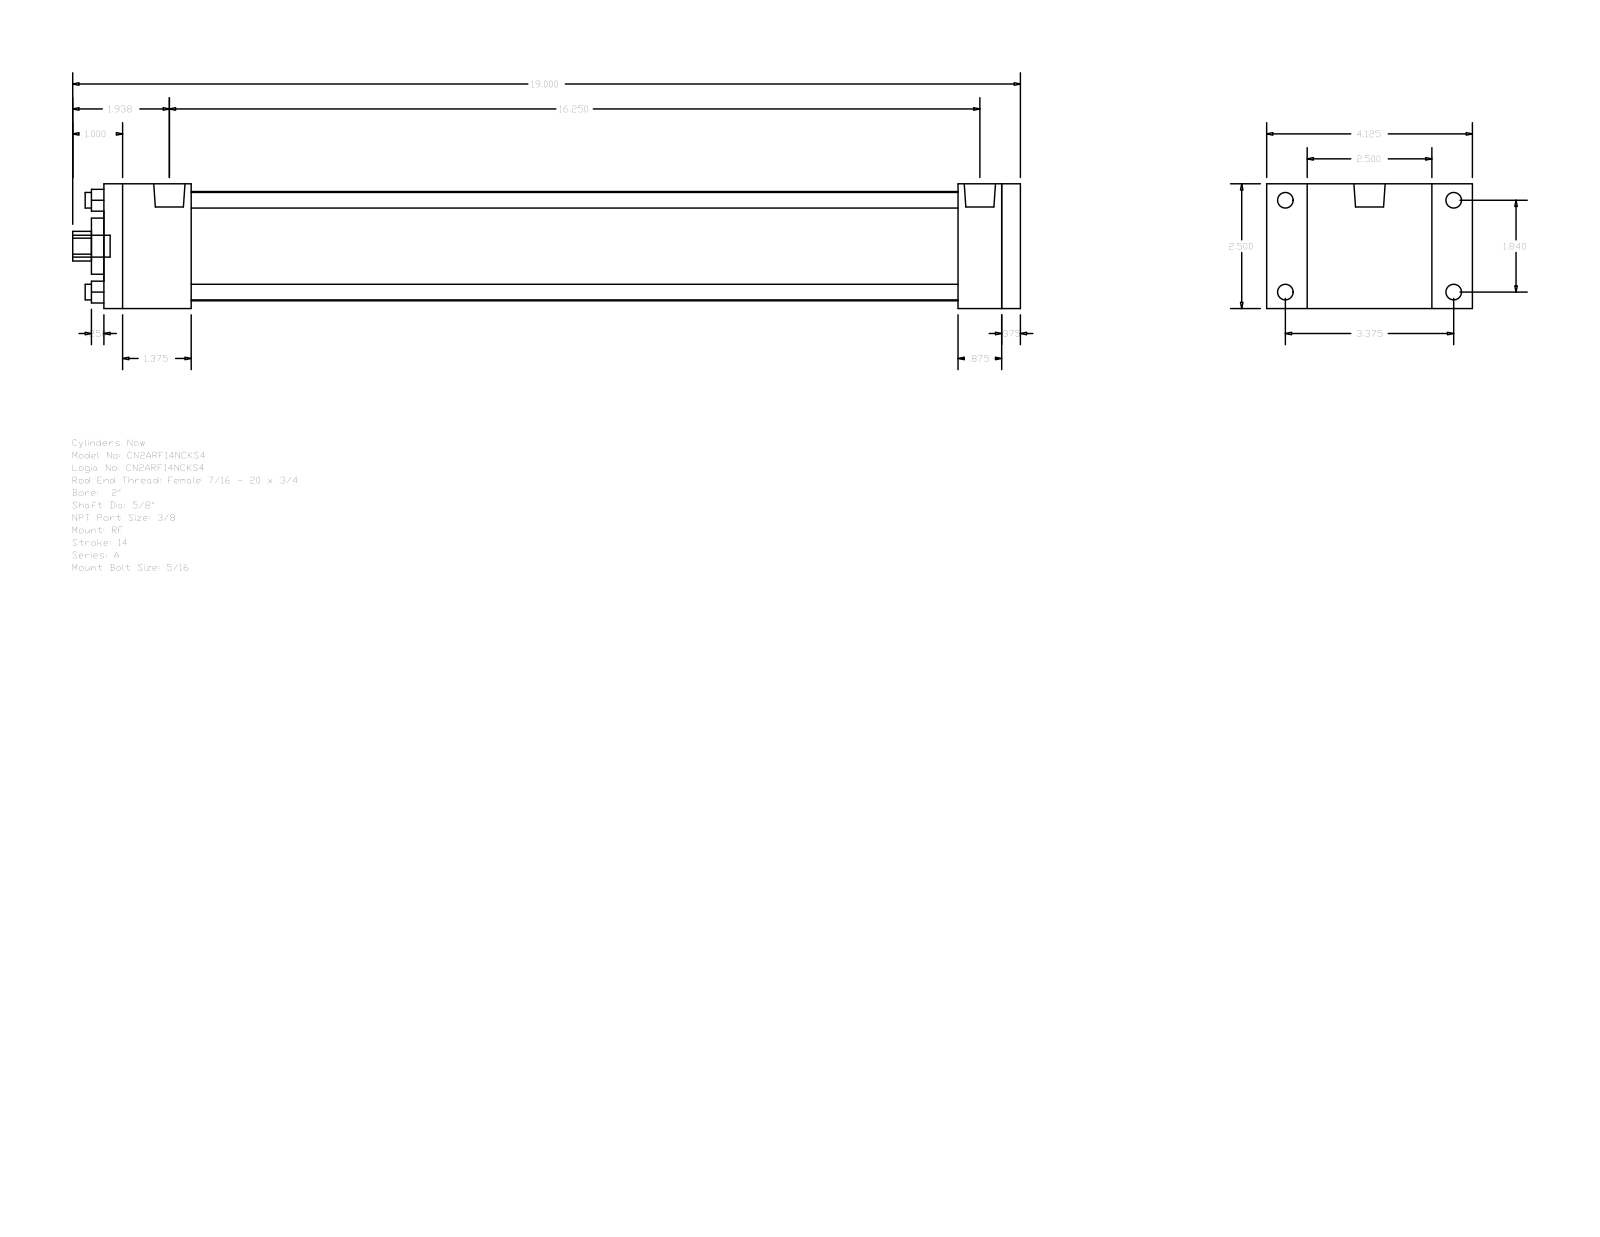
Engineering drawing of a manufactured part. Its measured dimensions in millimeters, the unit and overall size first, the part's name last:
Units: millimetres
Overall size (bounding box): 482.6 × 104.78 × 63.5
Round holes (diameter × count): ⌀7.94 ×4, ⌀15.88 ×1, ⌀28.57 ×1, ⌀55.63 ×1
Round bosses / shafts (diameter × count): ⌀7.94 ×4, ⌀5.56 ×4, ⌀15.93 ×2, ⌀11.11 ×1
Partial cylindrical surfaces — rounded edges, fillets, slot ends (radius × count): R7.54 ×1
Main face-to-face distances: 63.5, 466.72, 9.53, 457.19, 44.45, 412.74, 422.27, 434.97, 390.52, 22.22
Hole centre spacings: 33.05, 46.74, 66.1
Bodies: 0 solids, 92 faces (64 planar, 28 cylindrical, 0 other)
Part name (STEP PRODUCT): A_RF__0200_0.625
STEP written by: GSSL Pune (CONFIG_CONTROL_DESIGN)
